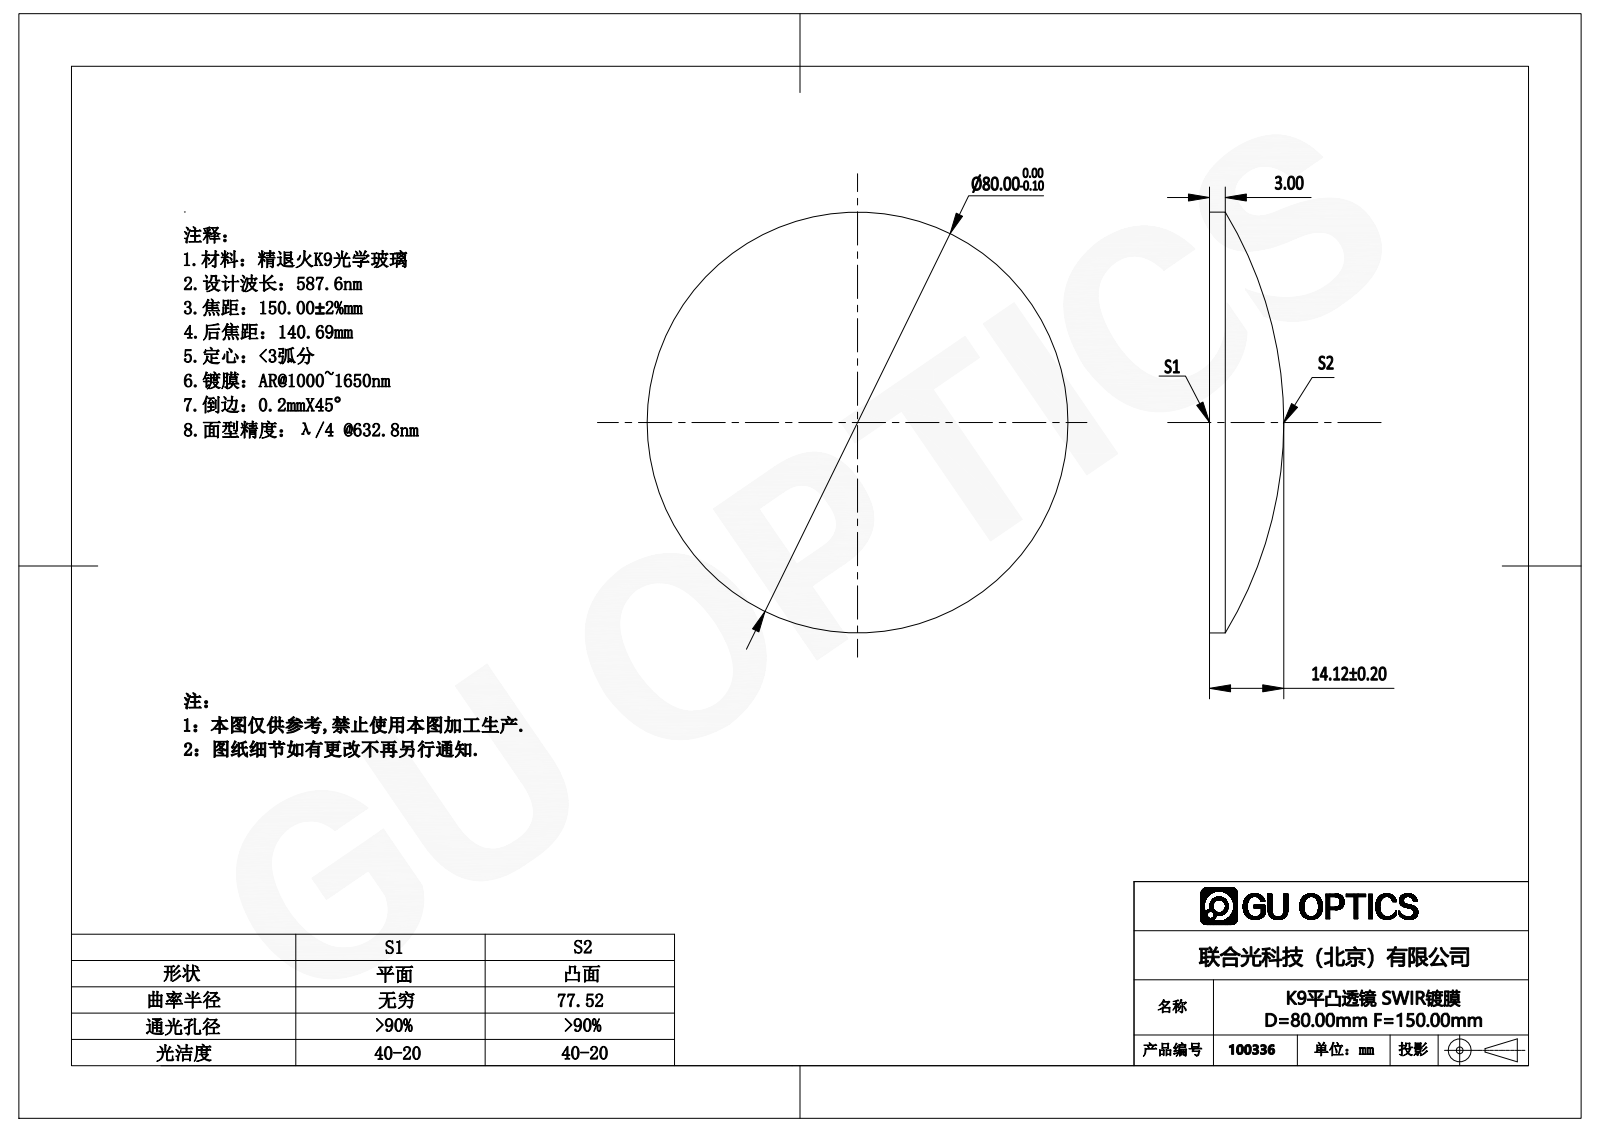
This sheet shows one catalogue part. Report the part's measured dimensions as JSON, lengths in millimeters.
{"part_name": "100164", "step_written_by": "SolidWorks 2016 (AUTOMOTIVE_DESIGN)", "units": "millimeters", "bodies": {"solids": 1, "faces": 5, "planar": 1, "cylindrical": 2, "other": 2}, "overall_size": [80, 80, 14.12], "volume_mm3": 43747, "surface_area_mm2": 11196, "round_bosses_or_shafts": [[80, 1]]}
